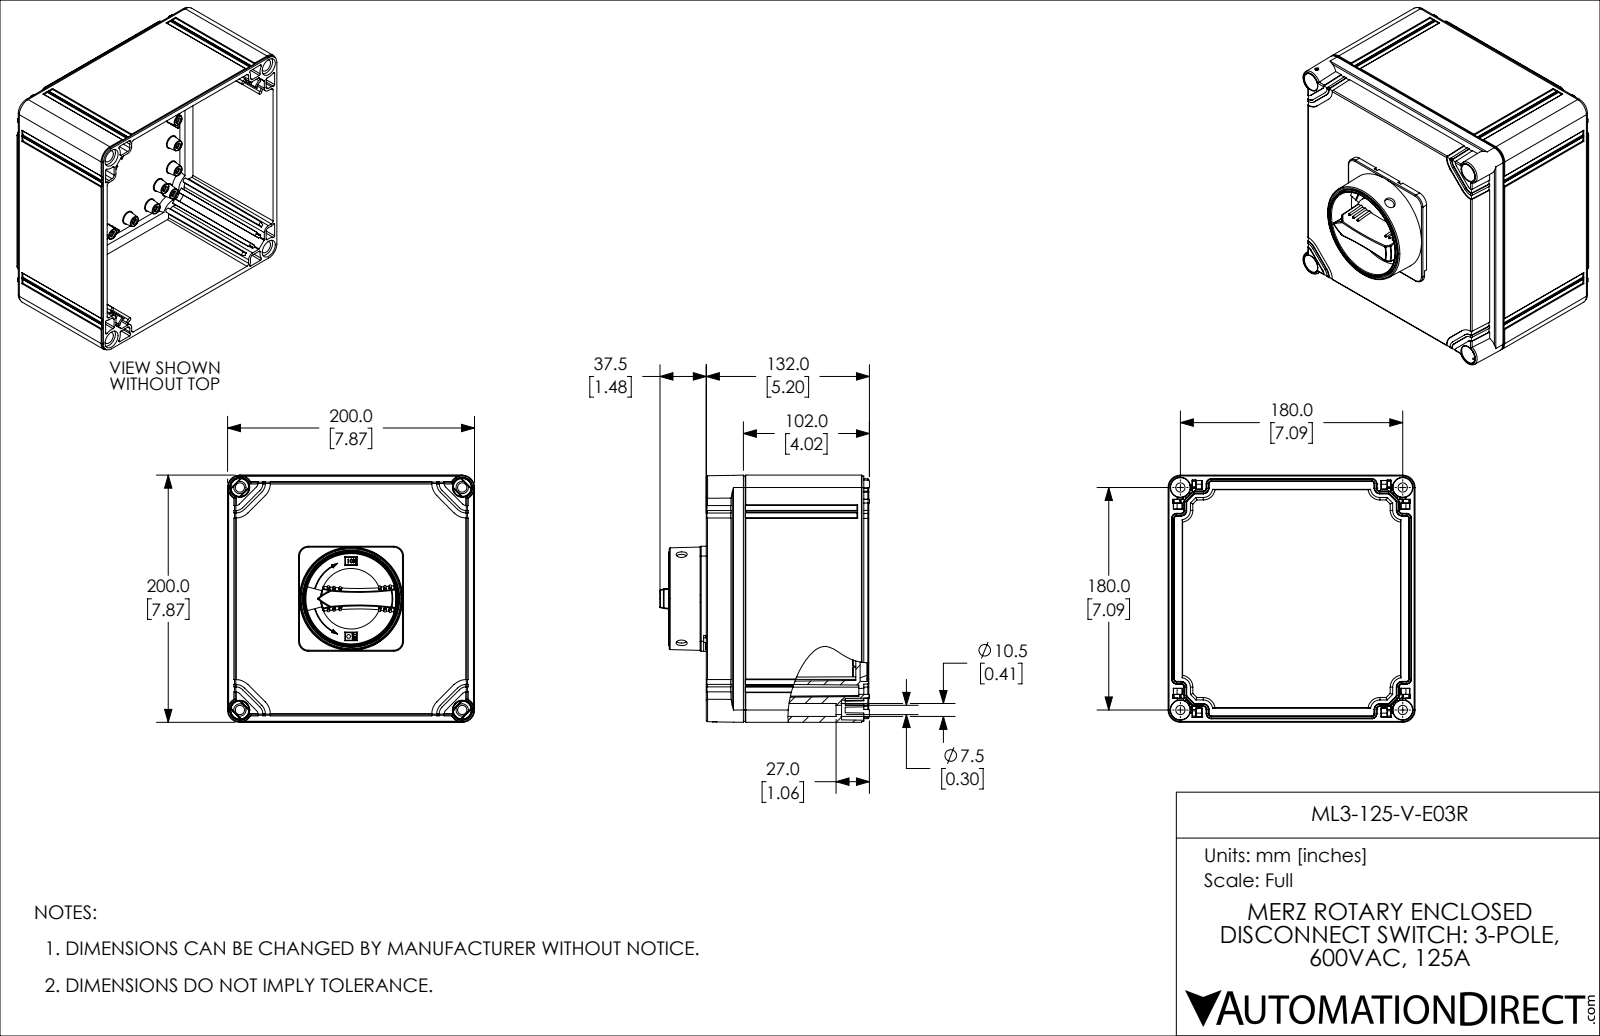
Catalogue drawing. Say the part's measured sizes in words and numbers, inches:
The part is named "ML3-125-V-E03R". Its 3-D file was written by "SolidWorks 2019 (AUTOMOTIVE_DESIGN)". It is 3 solids with 2645 faces: 1335 planar, 484 cylindrical and 826 other. Overall it measures 7.874 by 7.874 by 6.673 inches. Its volume is 113.5 cubic inches and its surface area 758.2 square inches. Round holes: 28 of diameter 0.165, 28 of diameter 0.197, 4 of diameter 0.295, 4 of diameter 0.394, 4 of diameter 0.413, 2 of diameter 0.087, 2 of diameter 0.157, 2 of diameter 0.354, 1 of diameter 0.807, 1 of diameter 1.772, 1 of diameter 2.878. Round bosses or shafts: 2 of diameter 0.315, 1 of diameter 3.031, 1 of diameter 3.012, 1 of diameter 1.929, 1 of diameter 1.87, 1 of diameter 0.323, 1 of diameter 0.15, 1 of diameter 0.118. Partial cylindrical surfaces (rounded edges, fillets, slot ends): 60 of radius 0.02, 16 of radius 0.008, 16 of radius 0.039, 16 of radius 0.067, 14 of radius 0.01, 13 of radius 0.315, 12 of radius 0.394, 8 of radius 0.157. The main face-to-face distances are 5.118, 0.138, 1.28, 3.839, 7.874, 3.701, 4.98, 0.217, 0.098, 5.256. The hole center spacings are 0.984, 5.987, 5.906, 0.71, 0.812, 1.499, 1.682, 1.783.
